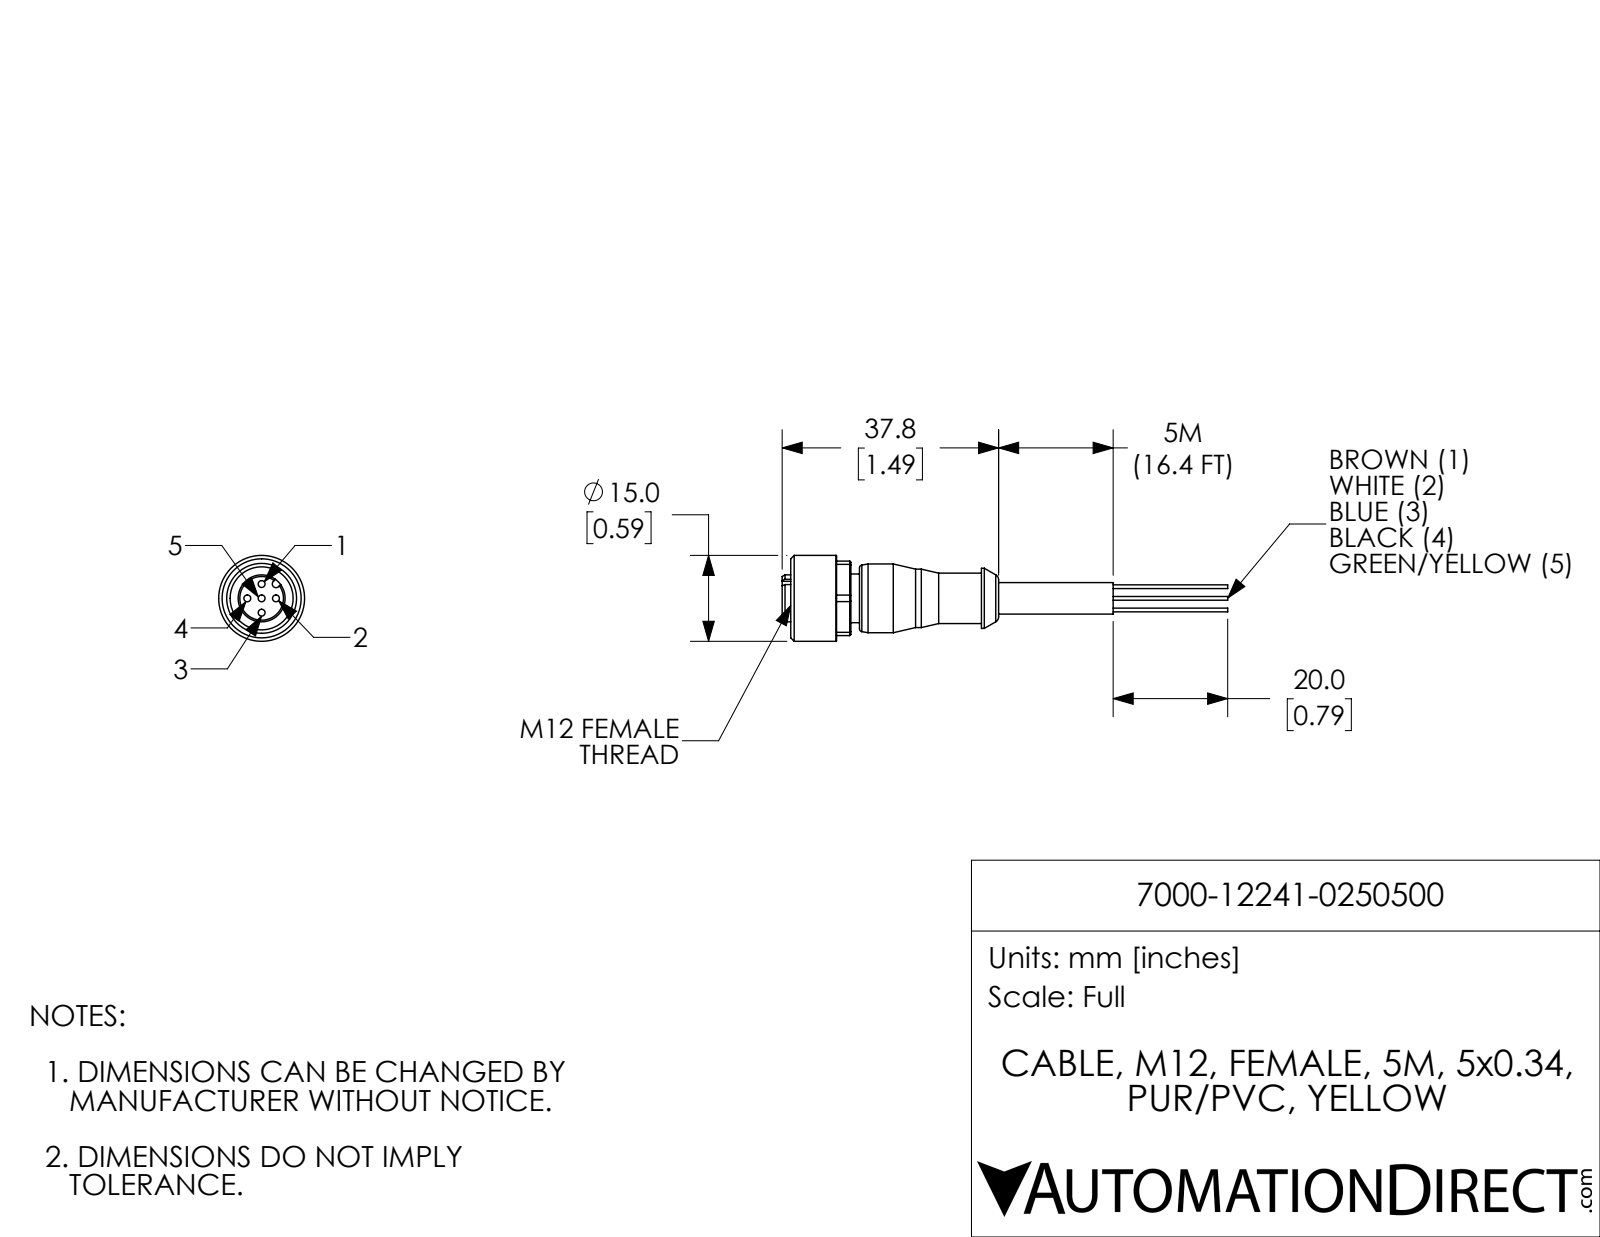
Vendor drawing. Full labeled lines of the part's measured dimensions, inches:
Part name (STEP PRODUCT): 7000-12241-0250500
STEP written by: SolidWorks 2017 (AUTOMOTIVE_DESIGN)
Units: inches
Bodies: 1 solid, 106 faces (34 planar, 45 cylindrical, 27 other)
Overall size (bounding box): 3.063 × 0.591 × 0.591
Volume: 0.248 in³ · Surface area: 4.45 in²
Round holes (diameter × count): ⌀0.047 ×5, ⌀0.433 ×1
Round bosses / shafts (diameter × count): ⌀0.026 ×5, ⌀0.591 ×1, ⌀0.472 ×1, ⌀0.413 ×1, ⌀0.402 ×1, ⌀0.346 ×1, ⌀0.335 ×1, ⌀0.323 ×1
Partial cylindrical surfaces — rounded edges, fillets, slot ends (radius × count): R0.026 ×1, R0.283 ×1
Main face-to-face distances: 0.472, 0.059, 0.118, 0.512, 0.354, 1.016, 0.295, 0.413, 0.098, 0.531
Hole centre spacings: 0.098, 0.139, 0.197
